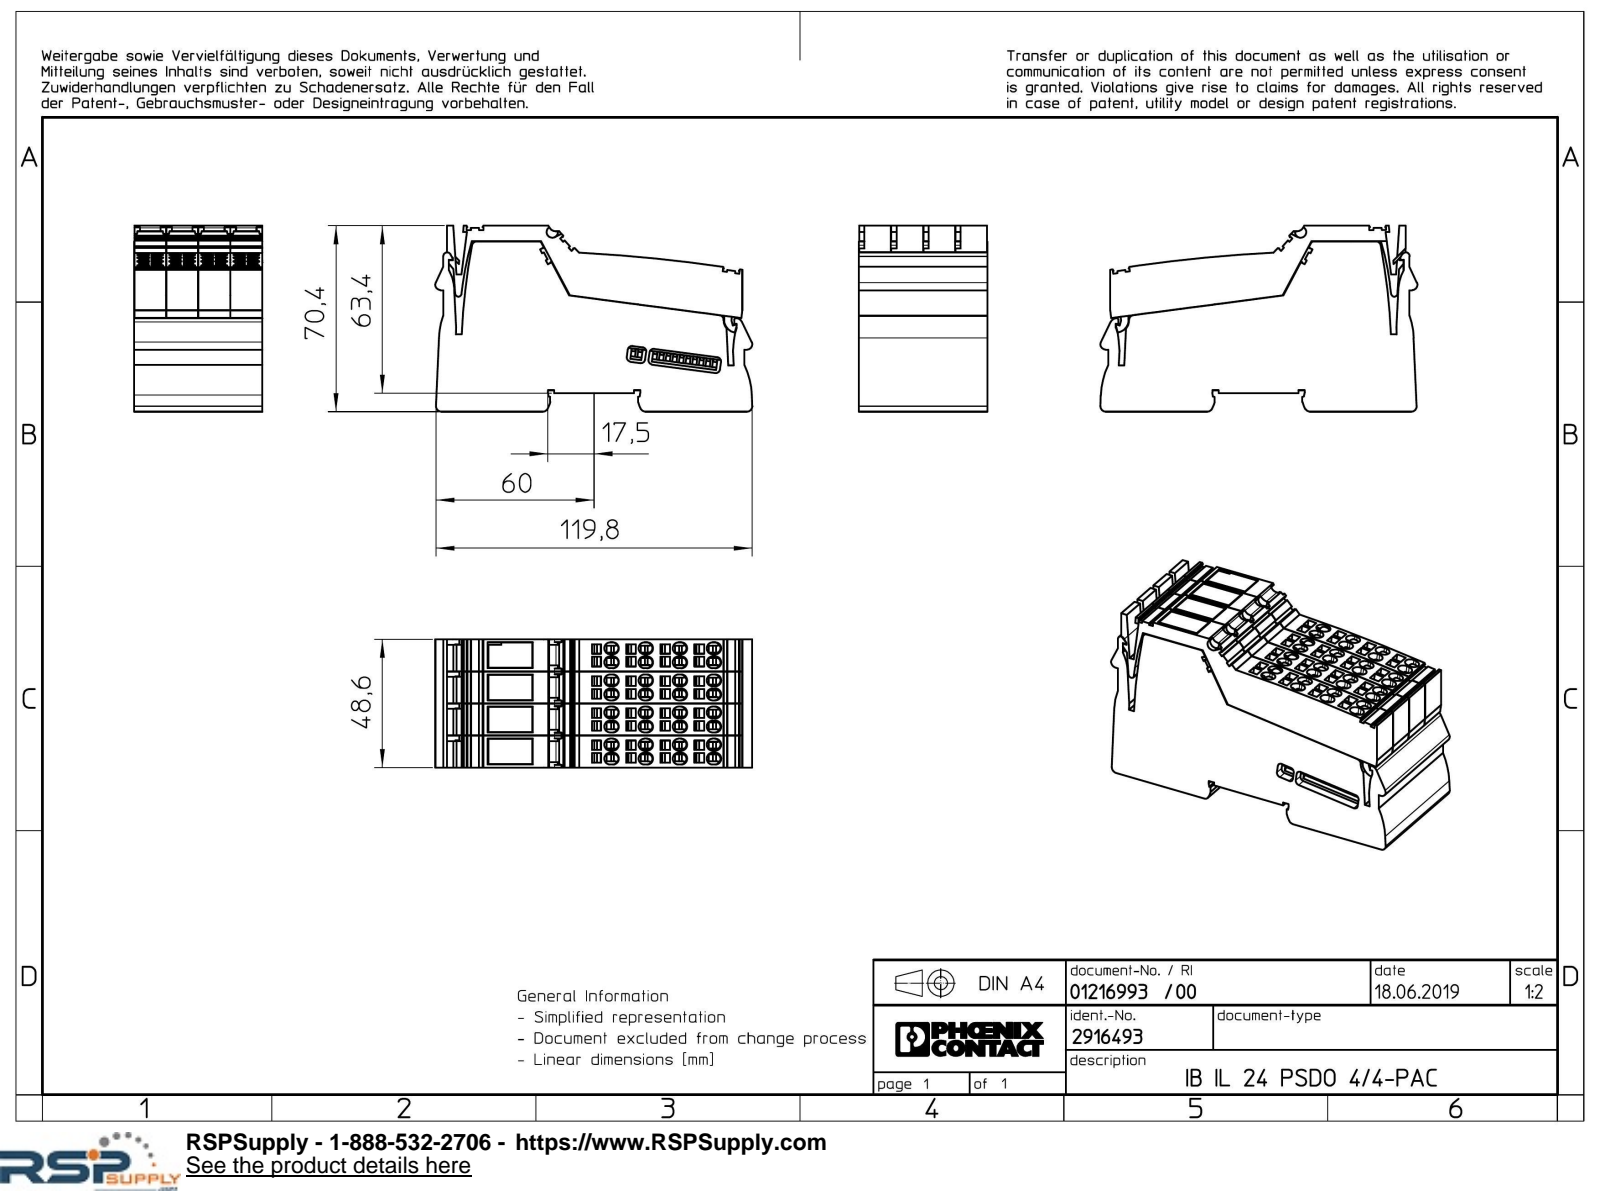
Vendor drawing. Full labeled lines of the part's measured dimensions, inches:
Part name (STEP PRODUCT): L_L_ST_YE_1018-select.2; L_L_8_GEH_GEFR_PSDI_PSDO_YE_1018-select; L_L_LWL_PK_HKS_21K_AUSSEN-select; L_L_LWL_PK_HKS_21K-select (+1 more)
STEP written by: Creo Elements/Direct Modeling 20.1A 29-Sep-2018 (C) Parametric Technology GmbH (AUTOMOTIVE_DESIGN)
Units: inches
Bodies: 9 solids, 2291 faces (1990 planar, 189 cylindrical, 112 other)
Overall size (bounding box): 4.729 × 2.773 × 1.913
Volume: 19.4 in³ · Surface area: 132.2 in²
Round holes (diameter × count): ⌀0.047 ×24
Partial cylindrical surfaces — rounded edges, fillets, slot ends (radius × count): R0.089 ×64, R0.024 ×8, R0.059 ×8, R0.079 ×6, R0.006 ×2, R0.067 ×2, R0.335 ×2, R0.374 ×2
Main face-to-face distances: 0.478, 0.957, 0.472, 1.913, 0.951, 1.435, 0.484, 1.429, 1.023, 0.512
Hole centre spacings: 0.701, 0.478, 0.512, 0.546, 1.085, 0.189, 0.588, 0.841
